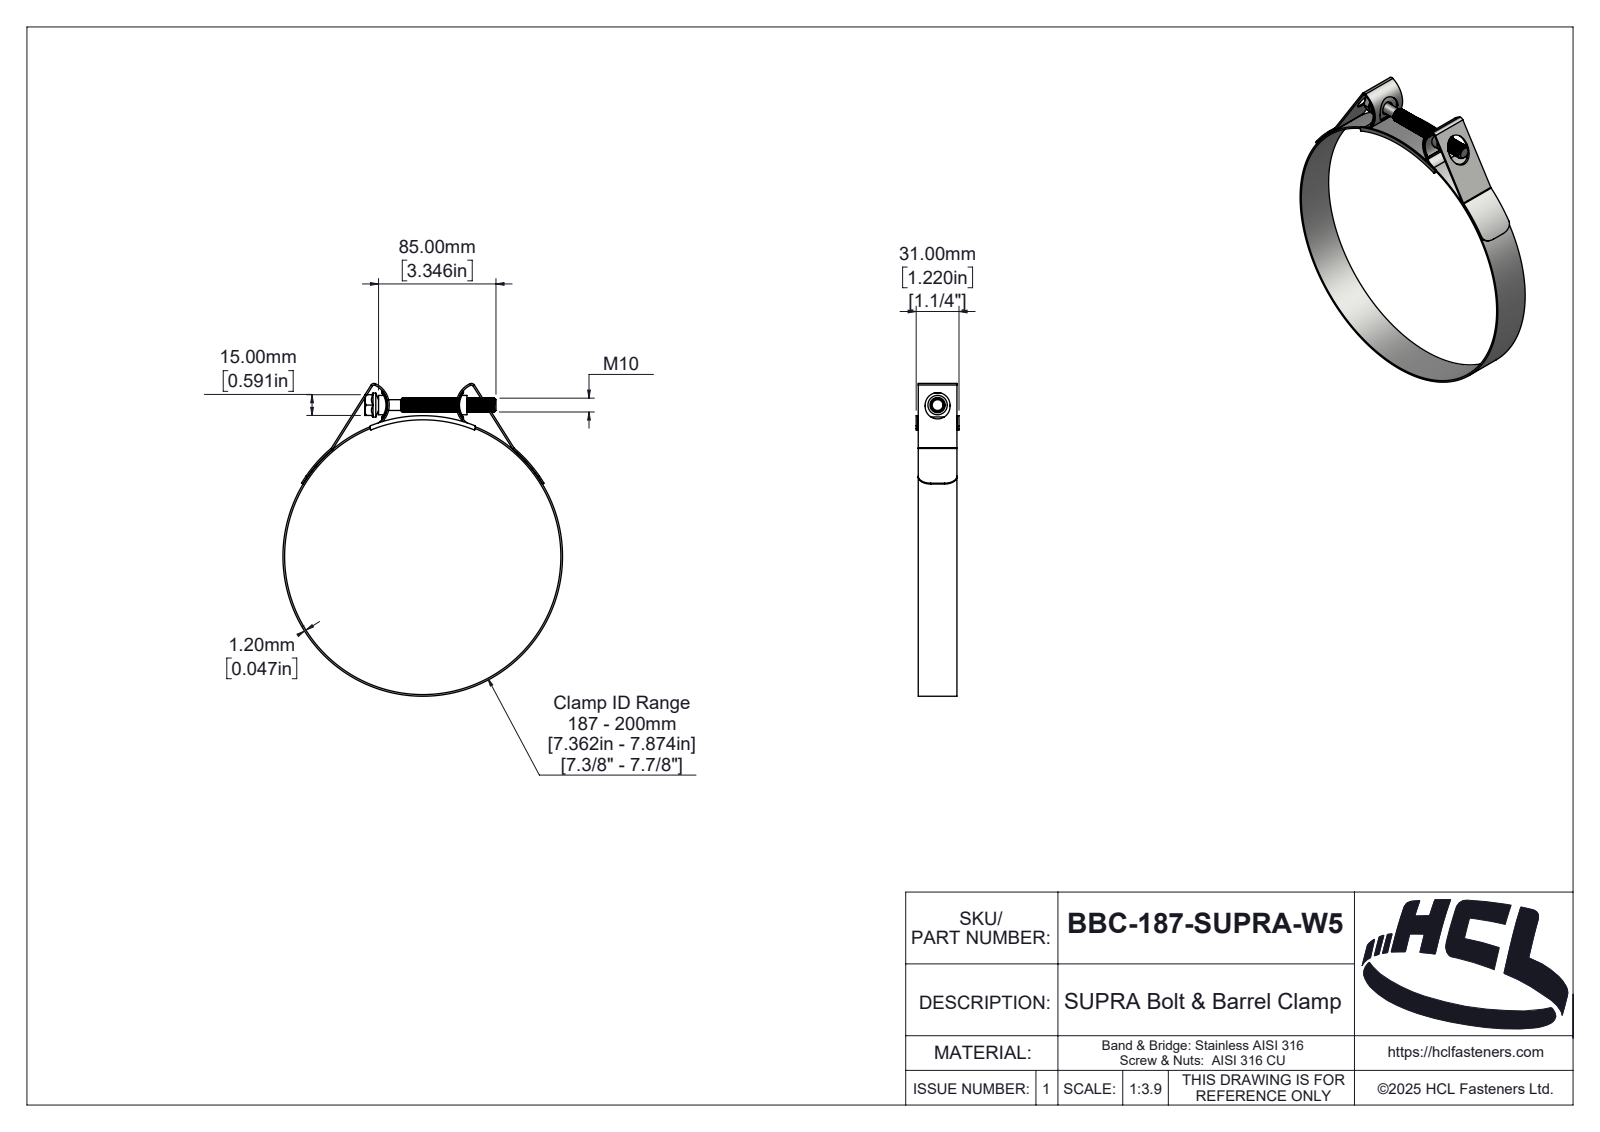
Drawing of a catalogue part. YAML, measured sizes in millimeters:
part_name: "BBC-187-SUPRA-W5"
step_written_by: "SolidWorks 2025 (AUTOMOTIVE_DESIGN)"
units: millimeters
bodies: {solids: 5, faces: 384, planar: 50, cylindrical: 247, other: 87}
overall_size: [226.34, 202.4, 31]
volume: 38424
surface_area: 58776
round_holes:
  - {diameter: 200, count: 1}
round_bosses_or_shafts:
  - {diameter: 202.4, count: 1}
  - {diameter: 17.32, count: 1}
  - {diameter: 14, count: 1}
  - {diameter: 10, count: 1}
  - {diameter: 7.8, count: 1}
partial_cylinders:
  - {radius: 1, count: 4}
  - {radius: 1.3, count: 2}
  - {radius: 2, count: 2}
  - {radius: 2.5, count: 2}
  - {radius: 3.2, count: 2}
  - {radius: 9, count: 2}
  - {radius: 14.68, count: 2}
  - {radius: 15.68, count: 2}
face_to_face_distances: [1.2, 28, 1.5, 29.5, 29.8, 28.3, 31, 28.6, 15, 2.5]
